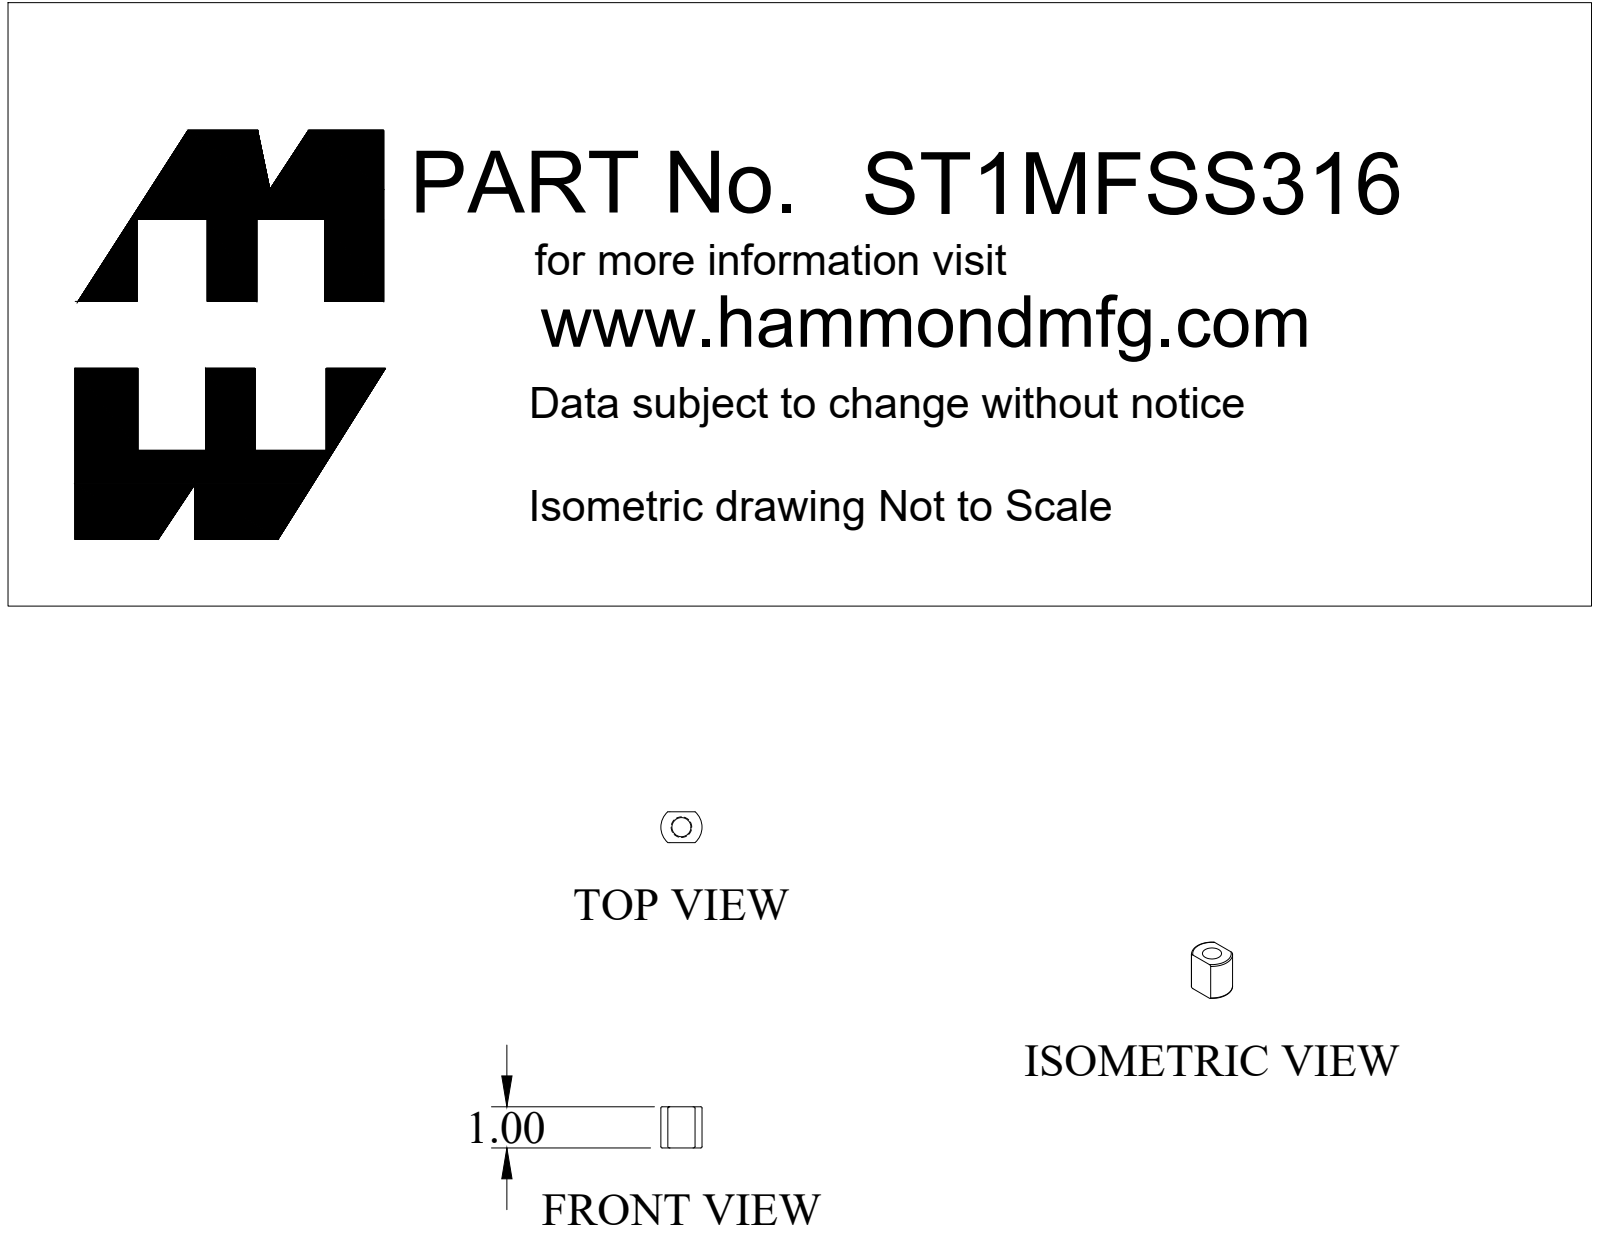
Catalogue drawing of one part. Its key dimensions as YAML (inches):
part_name: "ST1MFSS316"
step_written_by: "SolidWorks 2019 (CONFIG_CONTROL_DESIGN)"
units: inches
bodies: {solids: 3, faces: 26, planar: 15, cylindrical: 6, other: 5}
overall_size: [1.418, 1, 1]
volume: 0.855
surface_area: 9.941
round_holes:
  - {diameter: 0.465, count: 1}
  - {diameter: 0.532, count: 1}
round_bosses_or_shafts:
  - {diameter: 1, count: 1}
  - {diameter: 0.5, count: 1}
face_to_face_distances: [0.105, 0.75, 0.418, 0.313, 1, 1.105, 1.418, 0.742, 0.741, 0.355]
